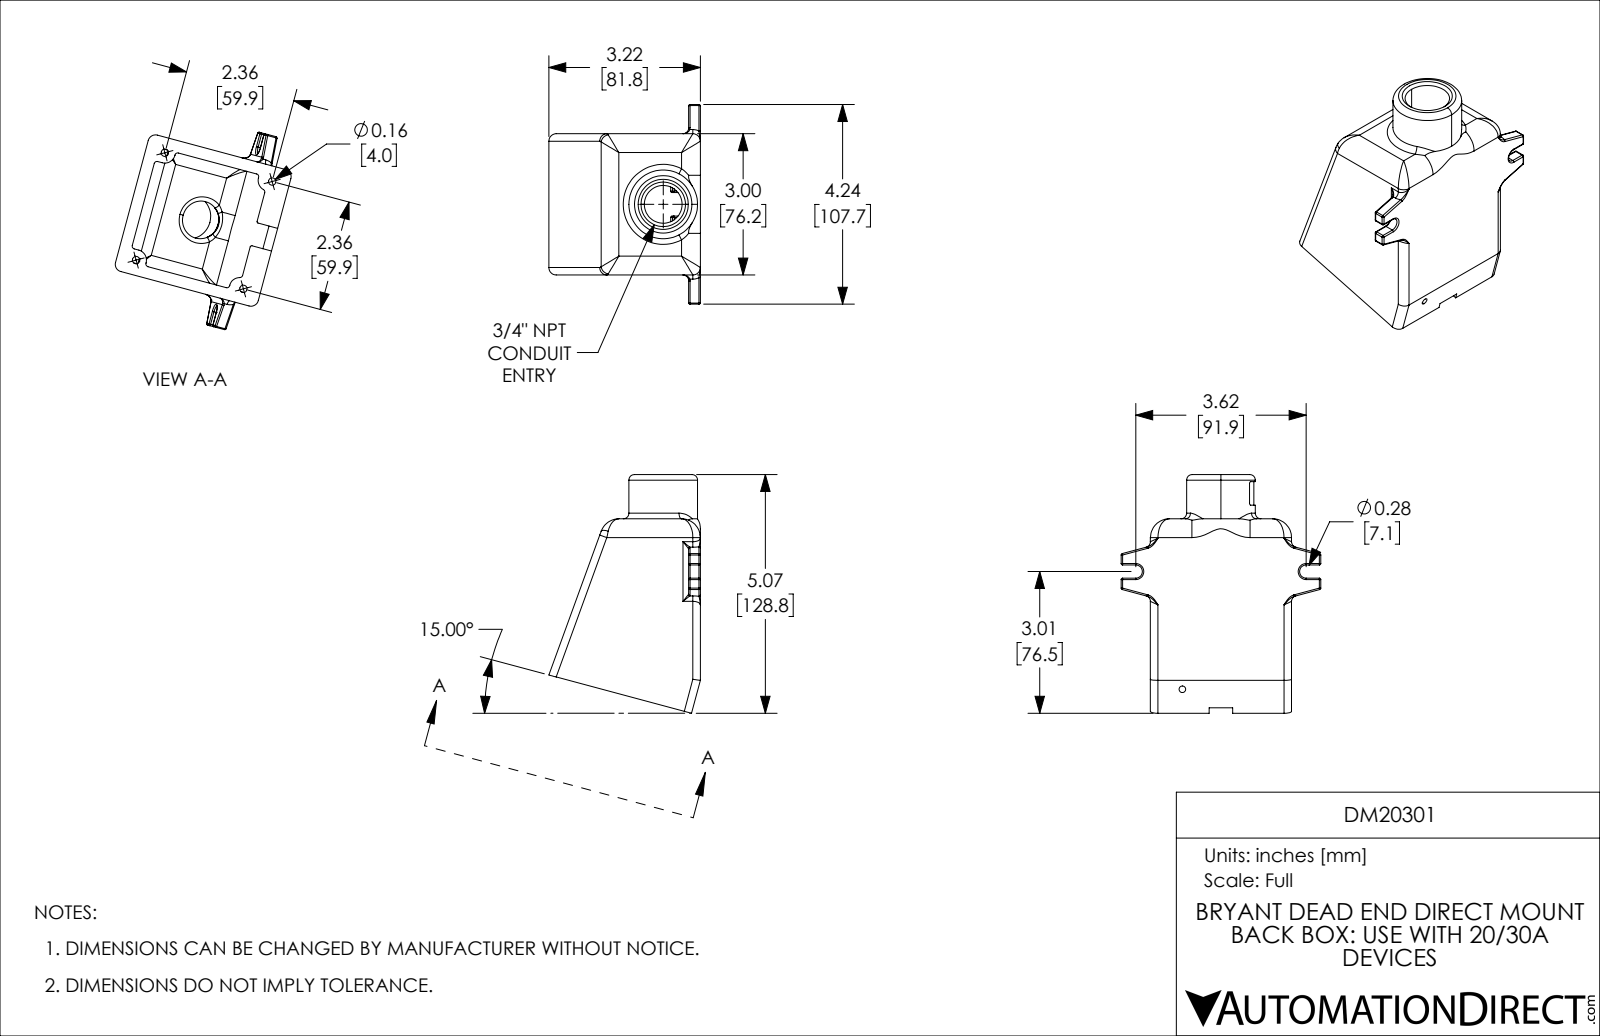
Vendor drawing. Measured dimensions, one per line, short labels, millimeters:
name: DM20301
written by: SolidWorks 2021 (CONFIG_CONTROL_DESIGN)
unit: mm
bodies: 1 solid, 329 faces (68 planar, 155 cylindrical, 106 other)
size: 128.78 × 107.7 × 81.79
volume: 156 876 mm³; area: 64 122 mm²
holes: 4× ⌀3.97, 1× ⌀3.52, 1× ⌀23.99, 1× ⌀28.45
bosses: 1× ⌀37.08
rounds: 61× R0.76, 13× R1.52, 6× R3.05, 6× R4.06, 4× R1.02, 4× R3.99, 4× R5.59, 4× R7.87
face distances: 4.83, 71.37, 76.2, 66.54, 4.82, 6.35, 1.52, 0.76, 4.07, 70.61
hole spacings: 59.94, 59.95, 84.77
